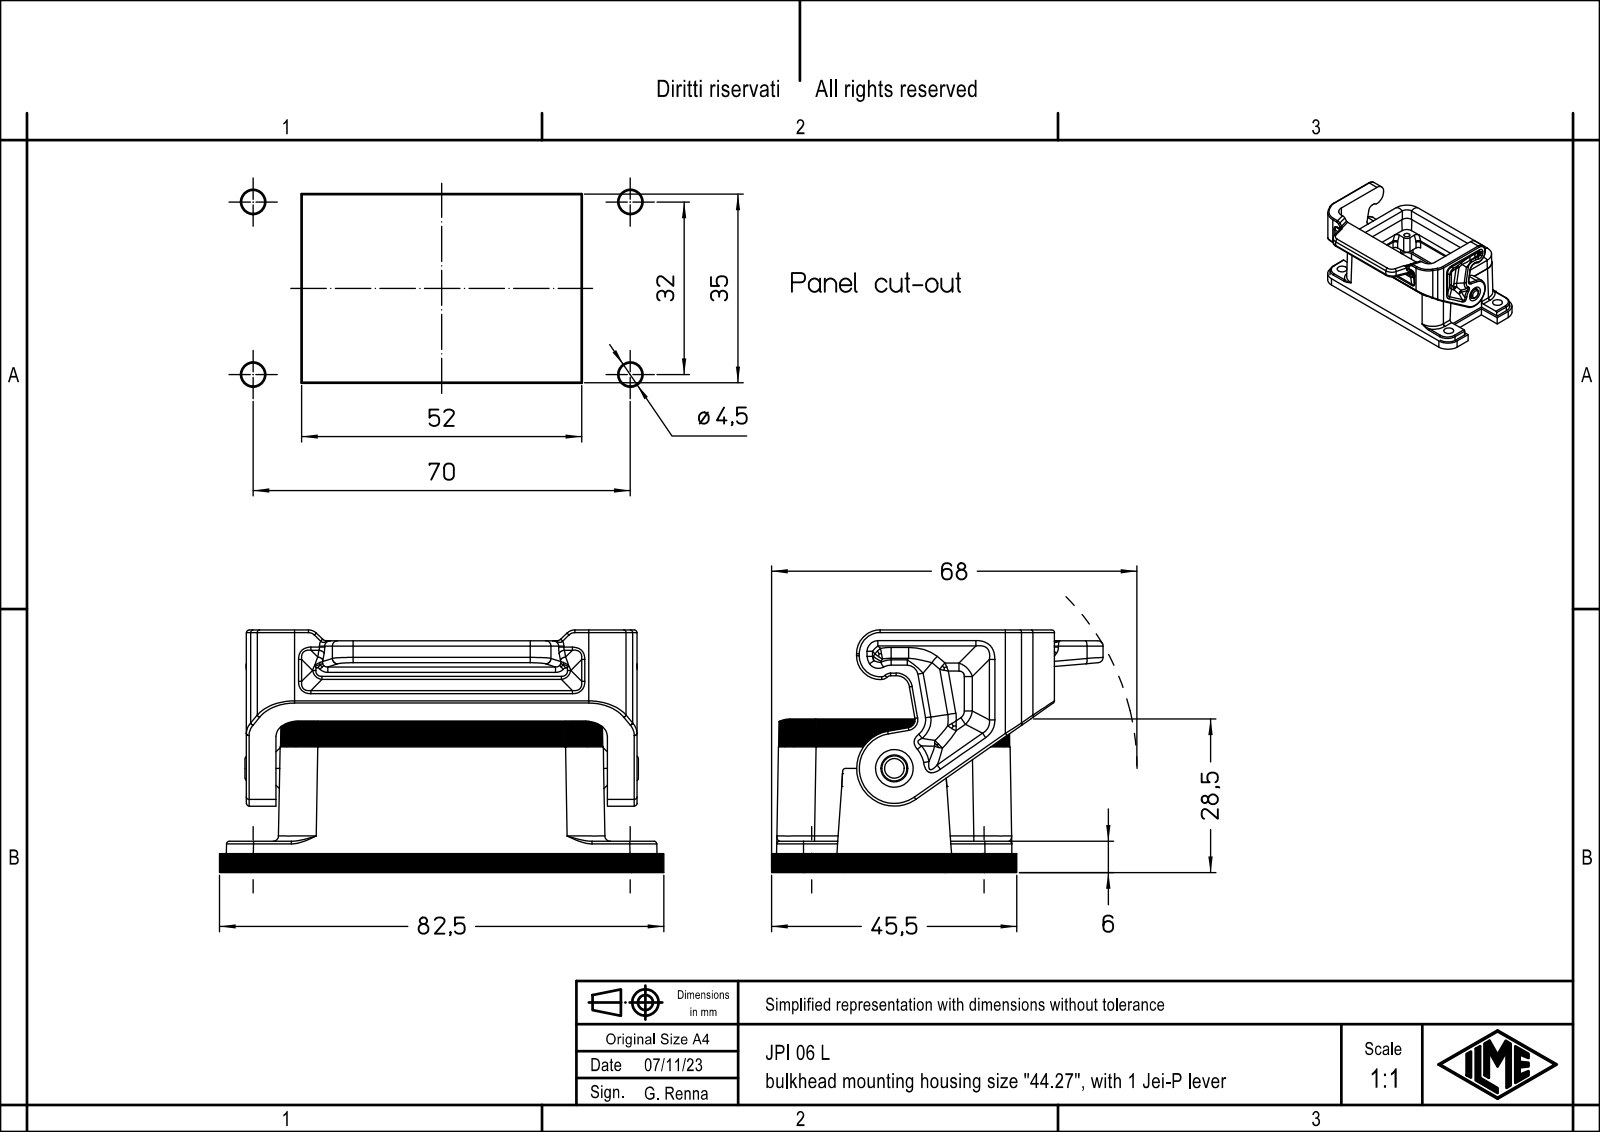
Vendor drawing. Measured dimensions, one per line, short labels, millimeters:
name: JPI 06 L
written by: Creo Elements/Direct Modeling 20.1B 02-Apr-2019 (C) Parametric Technology GmbH (AUTOMOTIVE_DESIGN)
unit: mm
bodies: 1 solid, 556 faces (164 planar, 198 cylindrical, 194 other)
size: 82.5 × 61.5 × 45
volume: 36 399 mm³; area: 23 392 mm²
holes: 4× ⌀2.75, 4× ⌀3.7
bosses: 1× ⌀4.65
rounds: 28× R0.5, 25× R1, 24× R3, 18× R1.5, 16× R2, 16× R4, 10× R5, 10× R6
face distances: 3.03, 61.5, 2, 3.5, 5, 43, 41.5, 5.5, 67, 39.5
hole spacings: 13.24, 32.24, 57.05, 64.18, 27, 32, 44, 51.62
